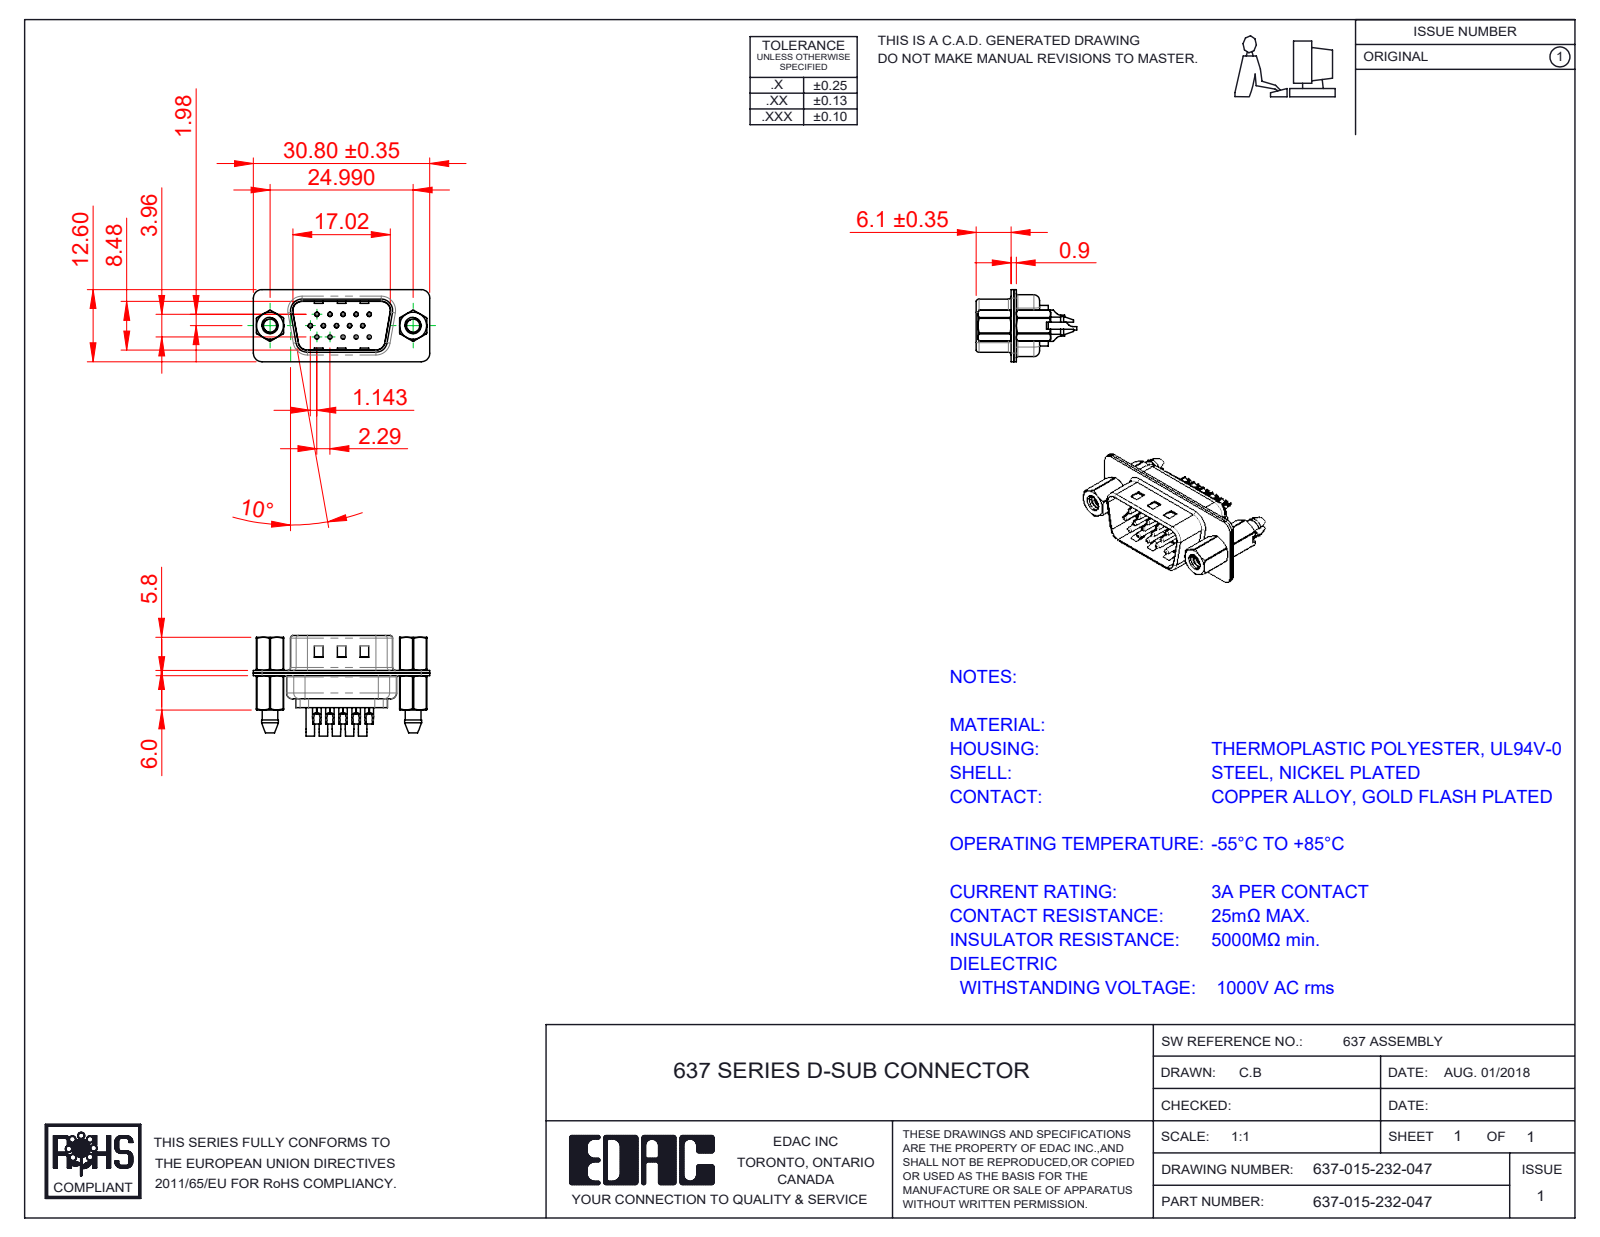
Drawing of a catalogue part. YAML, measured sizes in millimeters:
part_name: "637 Contact Row 3_32; 637 Shell Front_15 Contacts; 637 Contact Row 1_32; 637 4-40 Hex Standoff (+5 more)"
step_written_by: "SolidWorks 2020 (CONFIG_CONTROL_DESIGN)"
units: millimeters
bodies: {solids: 22, faces: 1464, planar: 371, cylindrical: 668, other: 425}
overall_size: [30.8, 17.55, 12.6]
volume: 1656
surface_area: 5547
round_holes:
  - {diameter: 0.35, count: 15}
  - {diameter: 1.1, count: 15}
  - {diameter: 1.6, count: 15}
  - {diameter: 2.26, count: 2}
  - {diameter: 2.29, count: 2}
  - {diameter: 4, count: 2}
  - {diameter: 4.8, count: 2}
round_bosses_or_shafts:
  - {diameter: 2, count: 15}
  - {diameter: 1.5, count: 15}
  - {diameter: 0.75, count: 15}
  - {diameter: 4.9, count: 2}
  - {diameter: 2.79, count: 2}
partial_cylinders:
  - {radius: 1.5, count: 18}
  - {radius: 2, count: 12}
  - {radius: 0.5, count: 8}
  - {radius: 1, count: 7}
  - {radius: 1.6, count: 6}
  - {radius: 0.25, count: 4}
  - {radius: 0.55, count: 4}
  - {radius: 0.7, count: 4}
face_to_face_distances: [0.45, 0.4, 0.9, 0.7, 4.76, 8.88, 8.48, 6.5, 1.05, 4.55]
hole_center_spacings: [3.96, 2.28, 4.57, 2.29, 6.05, 6.86, 7.92, 6.04]
